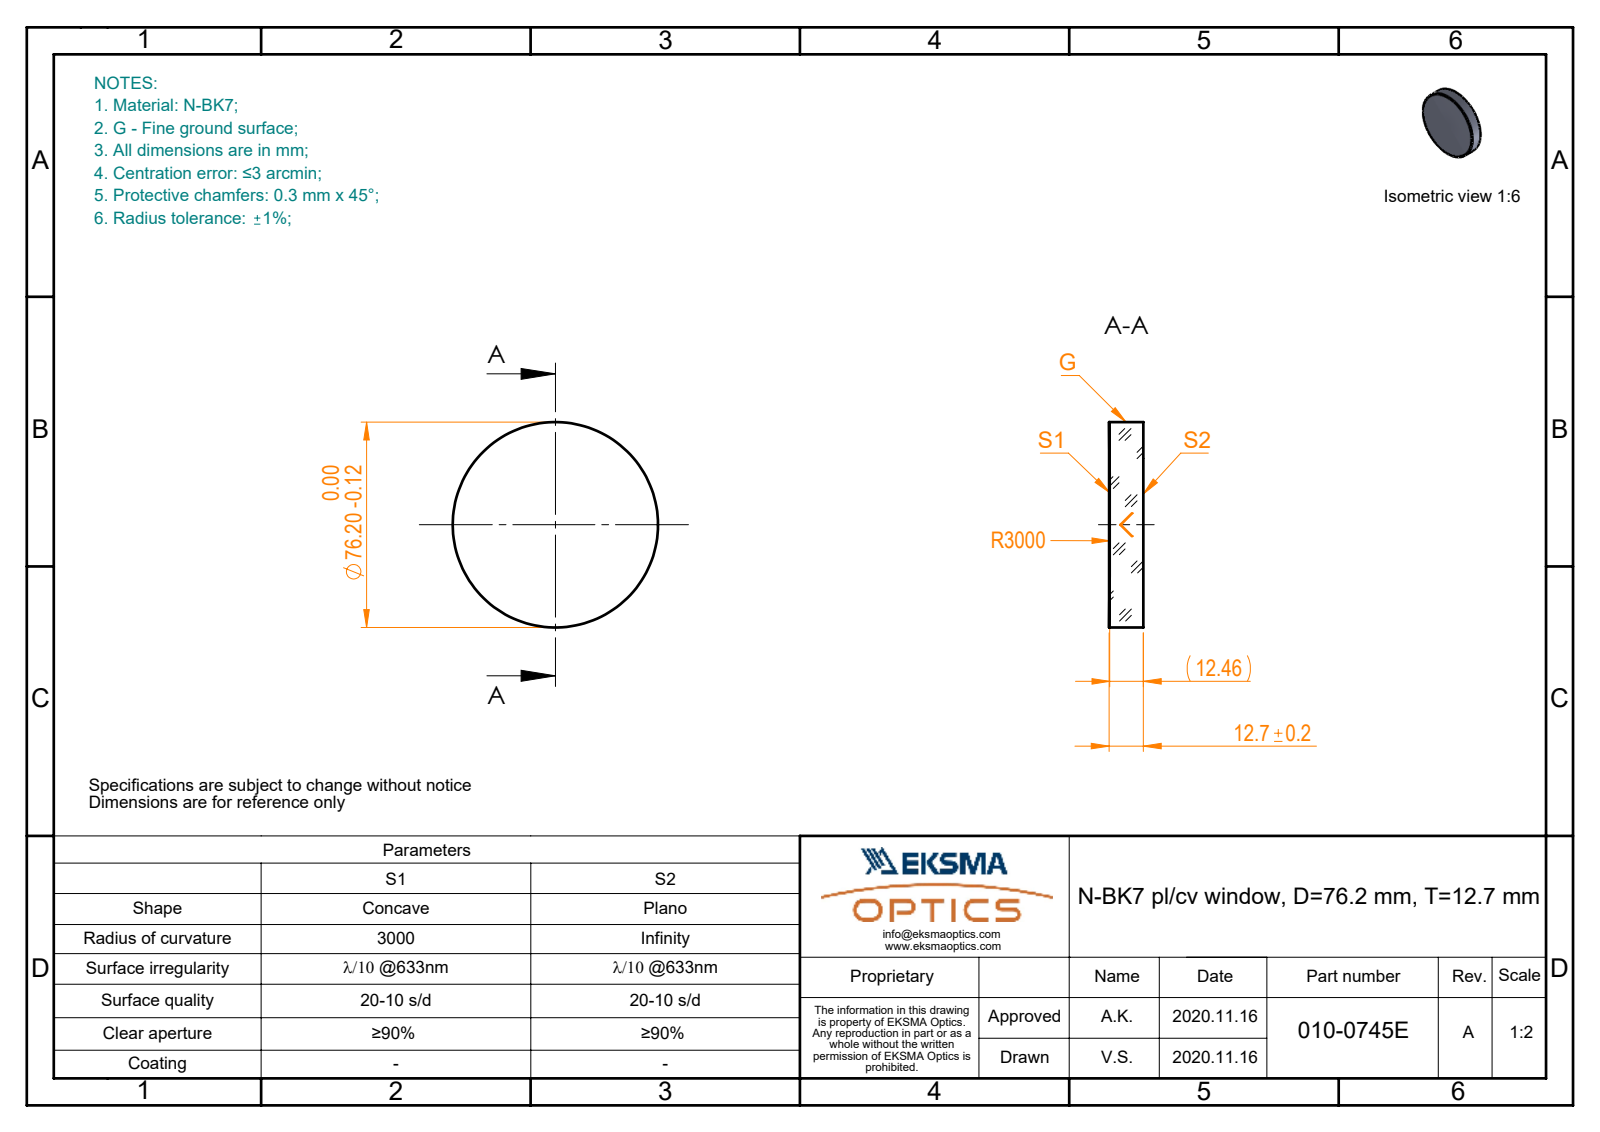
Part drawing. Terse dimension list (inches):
name: 010-0745E_N-BK7_PCV_window
written by: SolidWorks 2019 (CONFIG_CONTROL_DESIGN)
unit: in
bodies: 1 solid, 5 faces (1 planar, 2 cylindrical, 2 other)
size: 3 × 3 × 0.5
volume: 3.501 in³; area: 18.85 in²
bosses: 1× ⌀3
